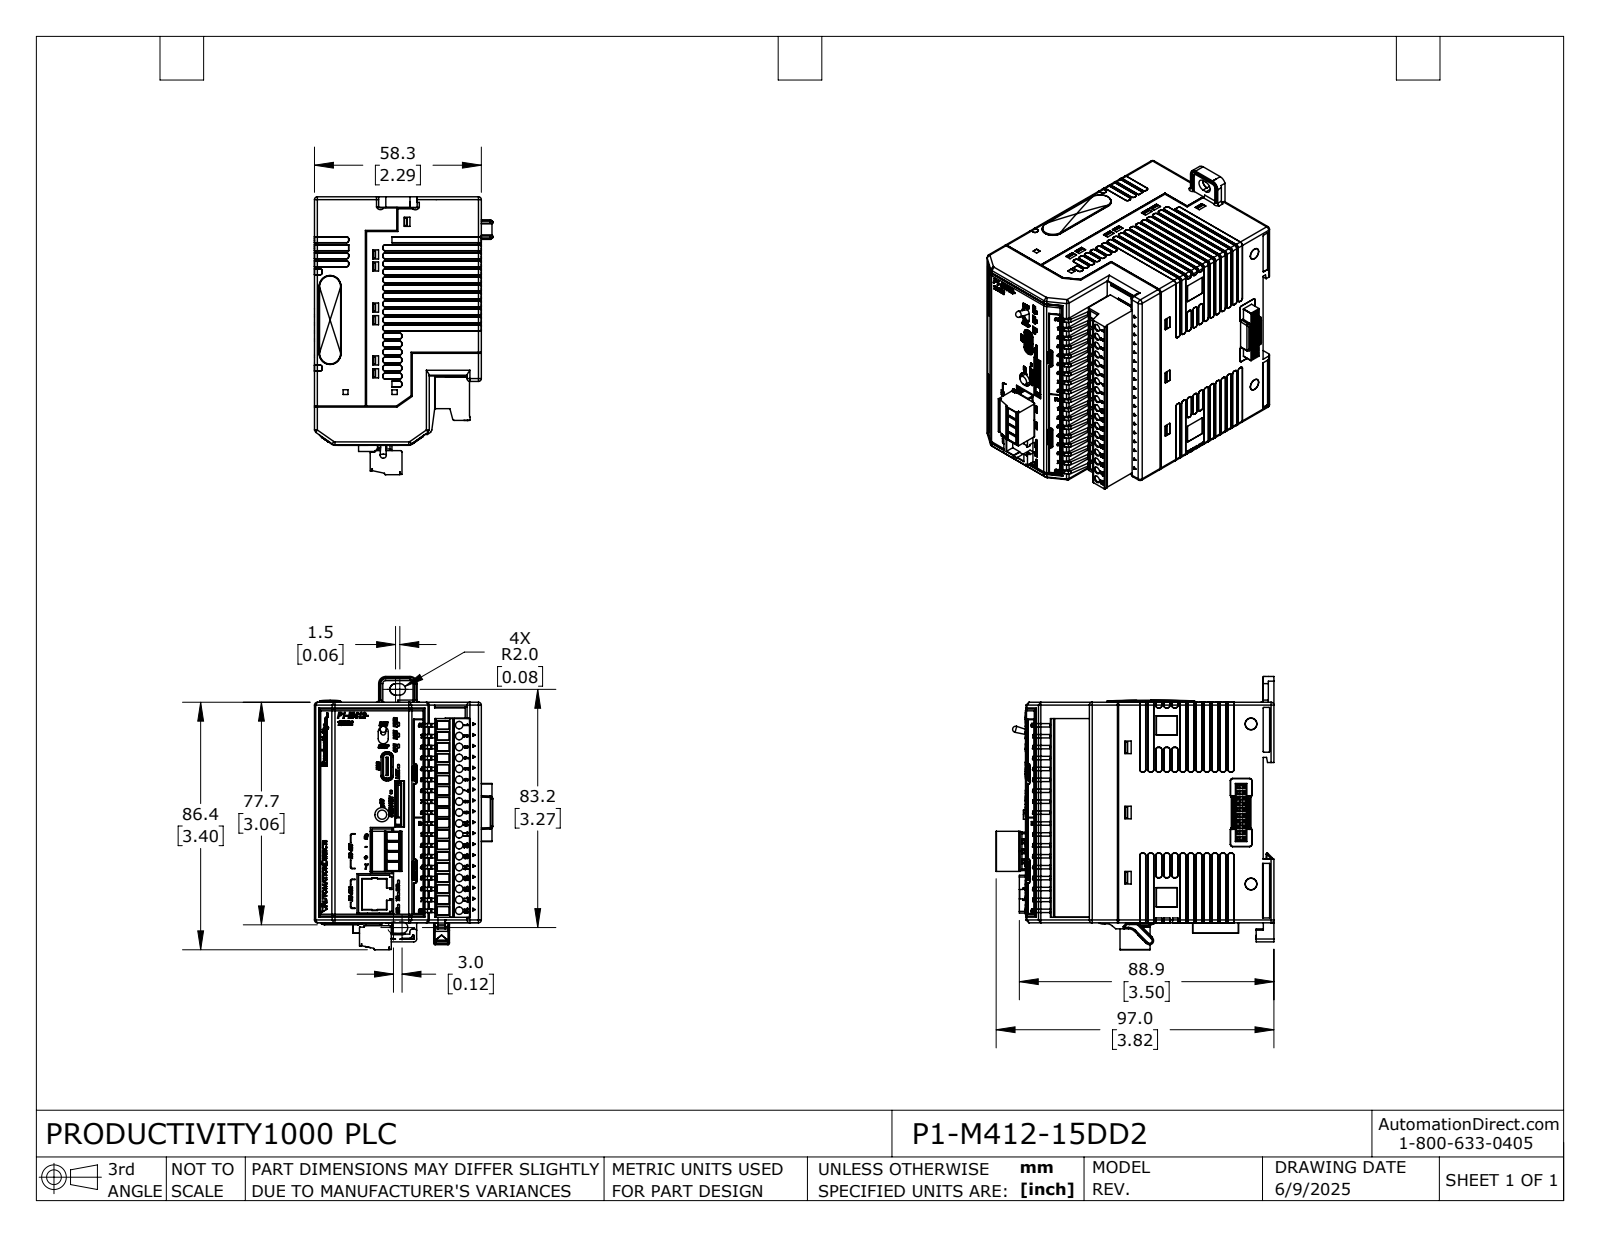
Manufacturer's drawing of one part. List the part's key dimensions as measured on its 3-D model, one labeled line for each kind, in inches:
Part name (STEP PRODUCT): P1-M412-15DD2
STEP written by: SolidWorks 2024 (AUTOMOTIVE_DESIGN)
Units: inches
Bodies: 24 solids, 3650 faces (2091 planar, 895 cylindrical, 664 other)
Overall size (bounding box): 3.686 × 3.593 × 2.452
Volume: 2.099 in³ · Surface area: 105 in²
Round holes (diameter × count): ⌀0.194 ×1
Round bosses / shafts (diameter × count): ⌀0.214 ×1, ⌀0.126 ×1
Partial cylindrical surfaces — rounded edges, fillets, slot ends (radius × count): R0.01 ×172, R0.008 ×86, R0.02 ×49, R0.039 ×33, R0.079 ×8, R0.024 ×7, R0.004 ×6, R0.012 ×4
Main face-to-face distances: 2.235, 0.02, 0.039, 2.275, 3.01, 3.022, 2.294, 2.294, 2.255, 3.02
